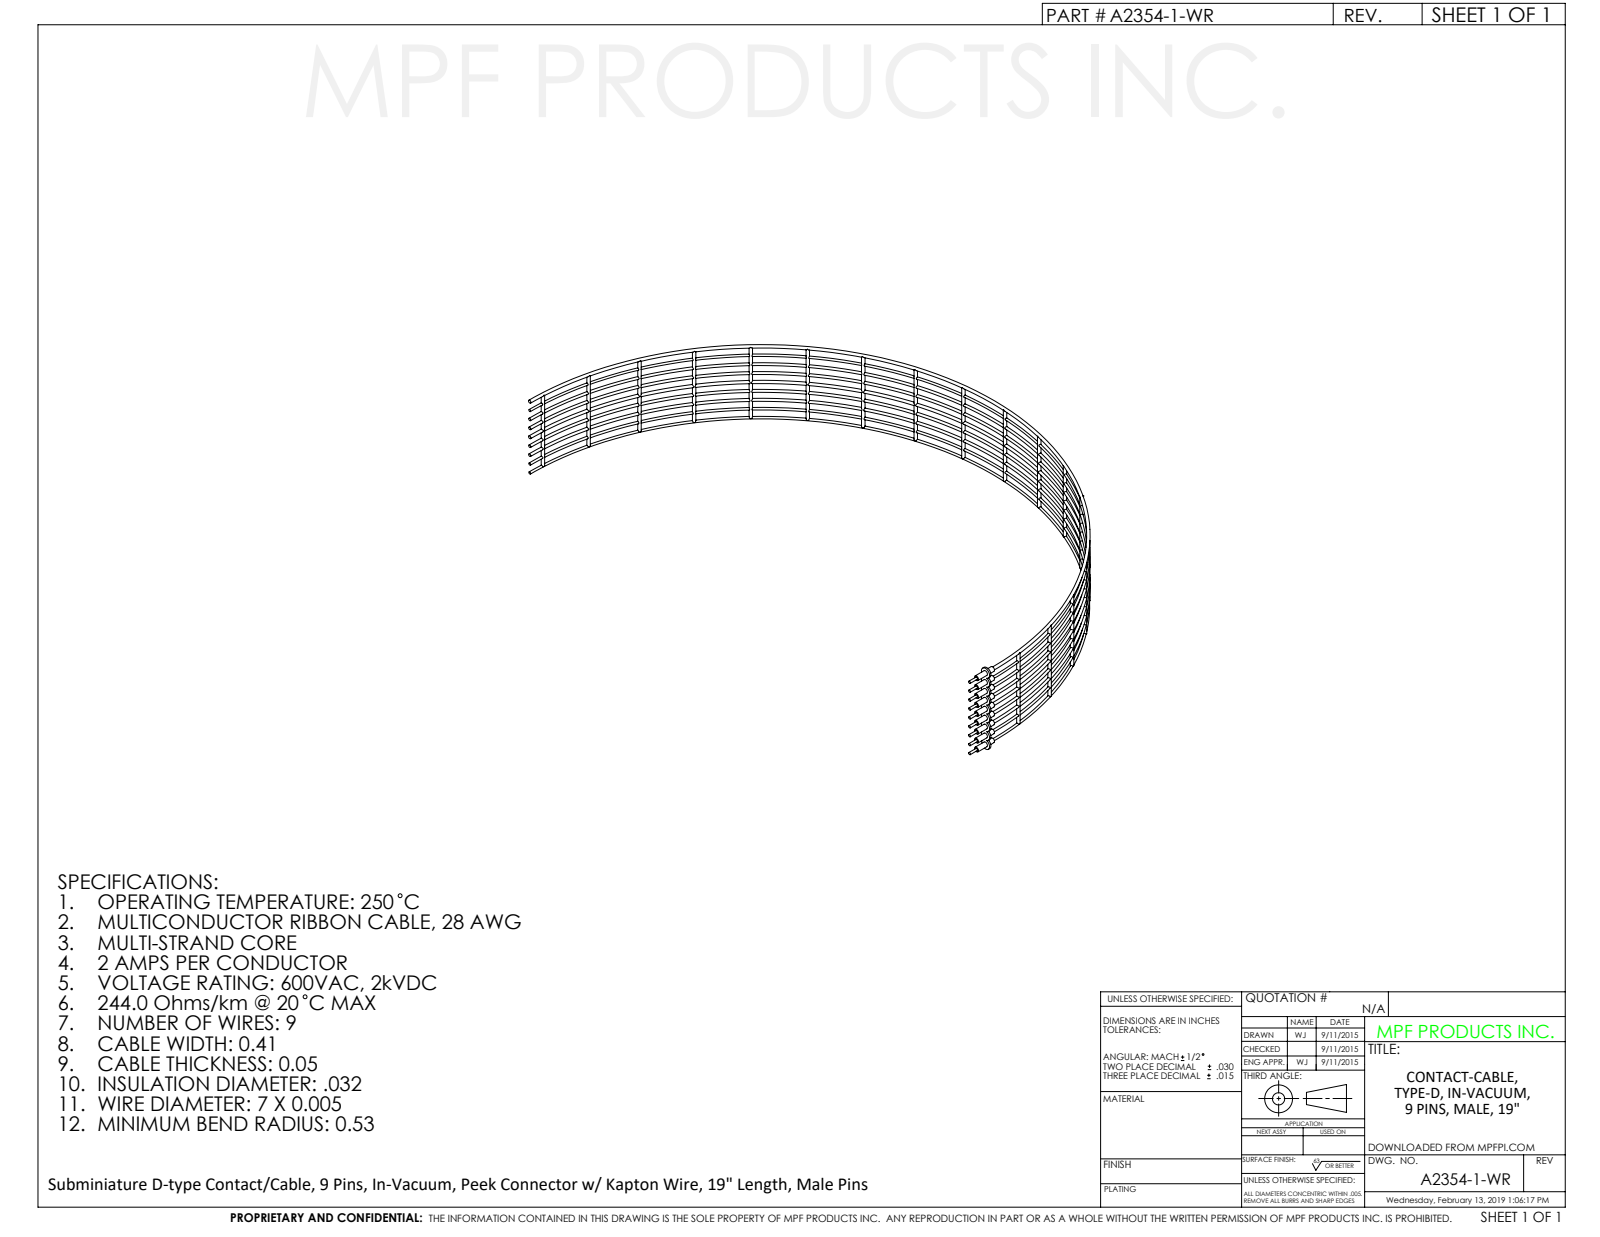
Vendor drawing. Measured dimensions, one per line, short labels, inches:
name: A2354-1-WR
written by: SolidWorks 2012 (CONFIG_CONTROL_DESIGN)
unit: in
bodies: 1 solid, 515 faces (75 planar, 116 cylindrical, 324 other)
size: 6.068 × 3.314 × 0.905
volume: 0.062 in³; area: 8.565 in²
bosses: 18× ⌀0.032, 9× ⌀0.05, 9× ⌀0.023, 8× ⌀0.105
rounds: 1× R0.053
face distances: 0.018, 0.074, 0.091, 0.207, 0.134, 0.116, 0.298, 0.225, 0.207, 0.091
